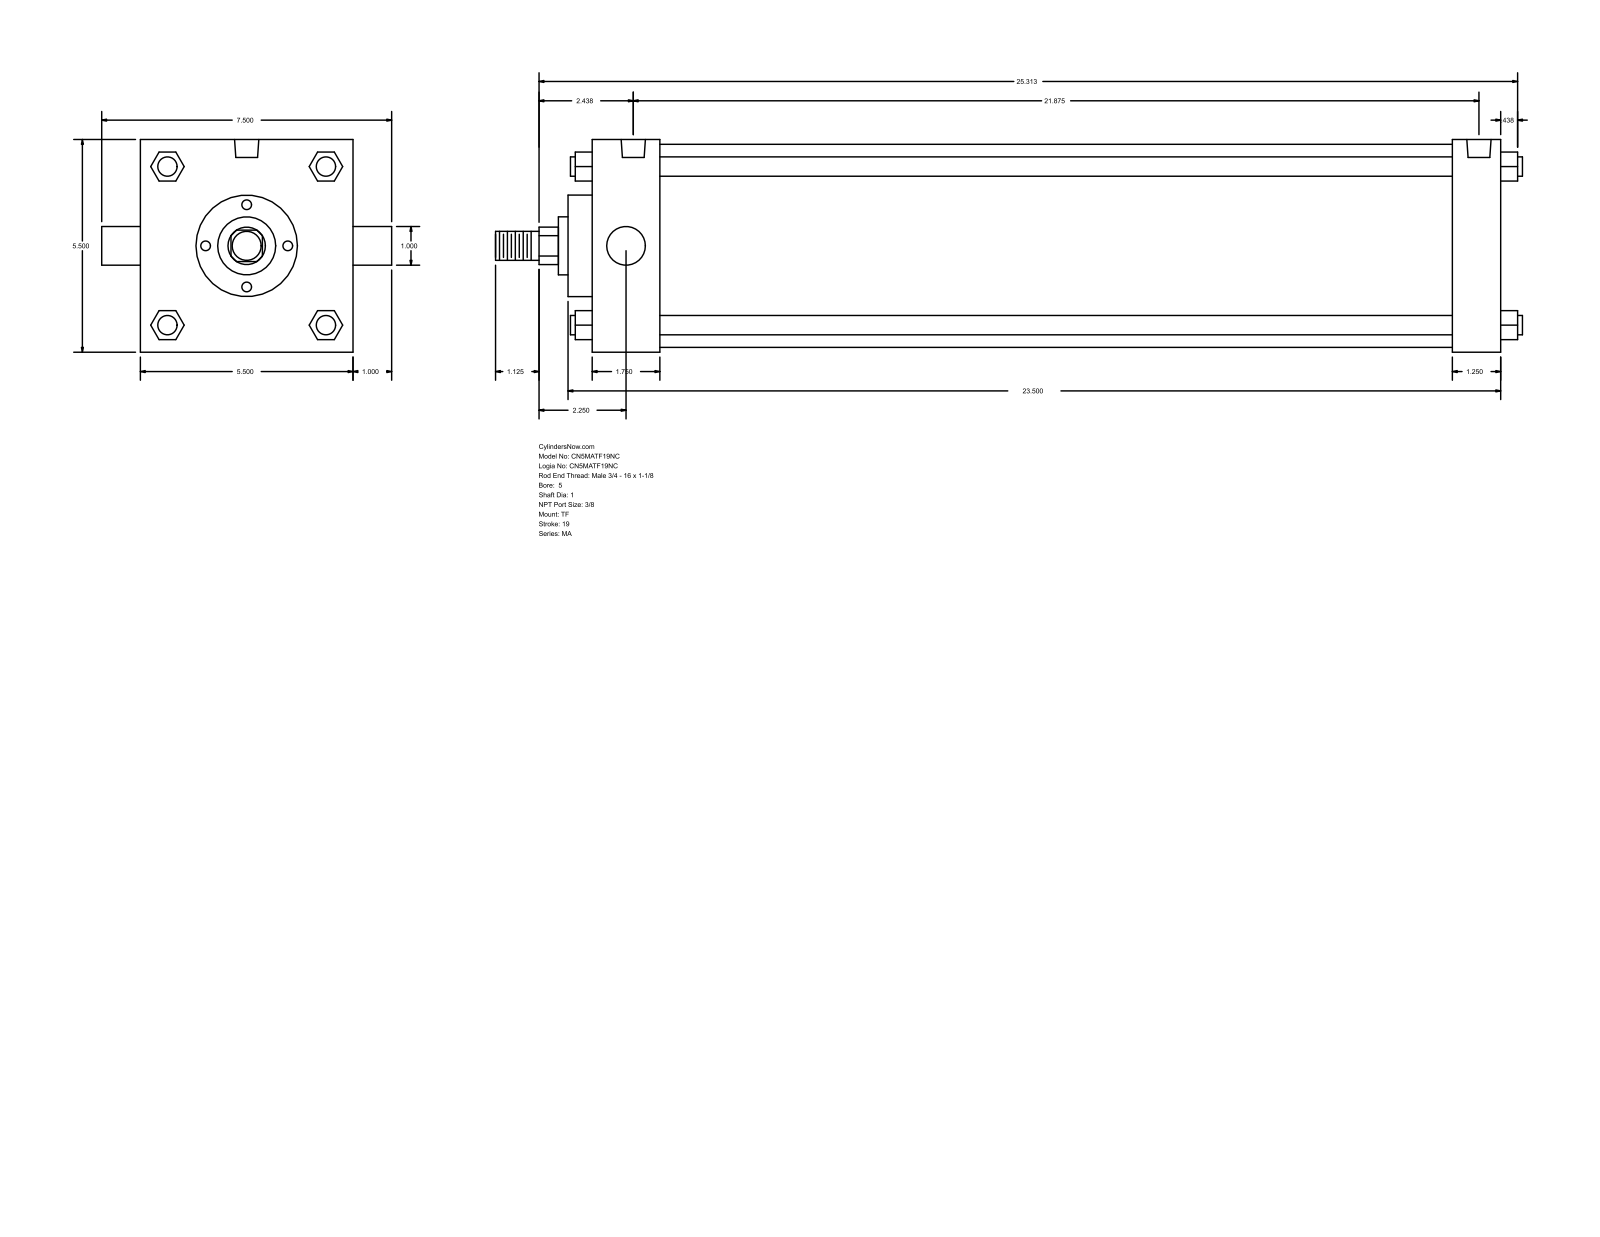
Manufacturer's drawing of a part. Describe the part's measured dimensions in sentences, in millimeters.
The part is named "MA_TF__0500_1". Its 3-D file was written by "GSSL Pune (CONFIG_CONTROL_DESIGN)". It is 0 solids with 122 faces: 93 planar, 29 cylindrical and 0 other. Overall it measures 674.69 by 190.5 by 139.7 millimeters. Round holes: 3 of diameter 11.11, 2 of diameter 15.93. Round bosses or shafts: 4 of diameter 12.7, 2 of diameter 25.4, 1 of diameter 133.35, 1 of diameter 66.67, 1 of diameter 38.1, 1 of diameter 19.05. Partial cylindrical surfaces (rounded edges, fillets, slot ends): 1 of radius 12.29. The main face-to-face distances are 139.7, 596.91, 565.16, 31.75, 44.46, 520.7, 552.45, 15.87, 60.33, 581.03. The hole center spacings are 4.76, 4.77, 546.1, 550.86, 550.87, 555.63.
